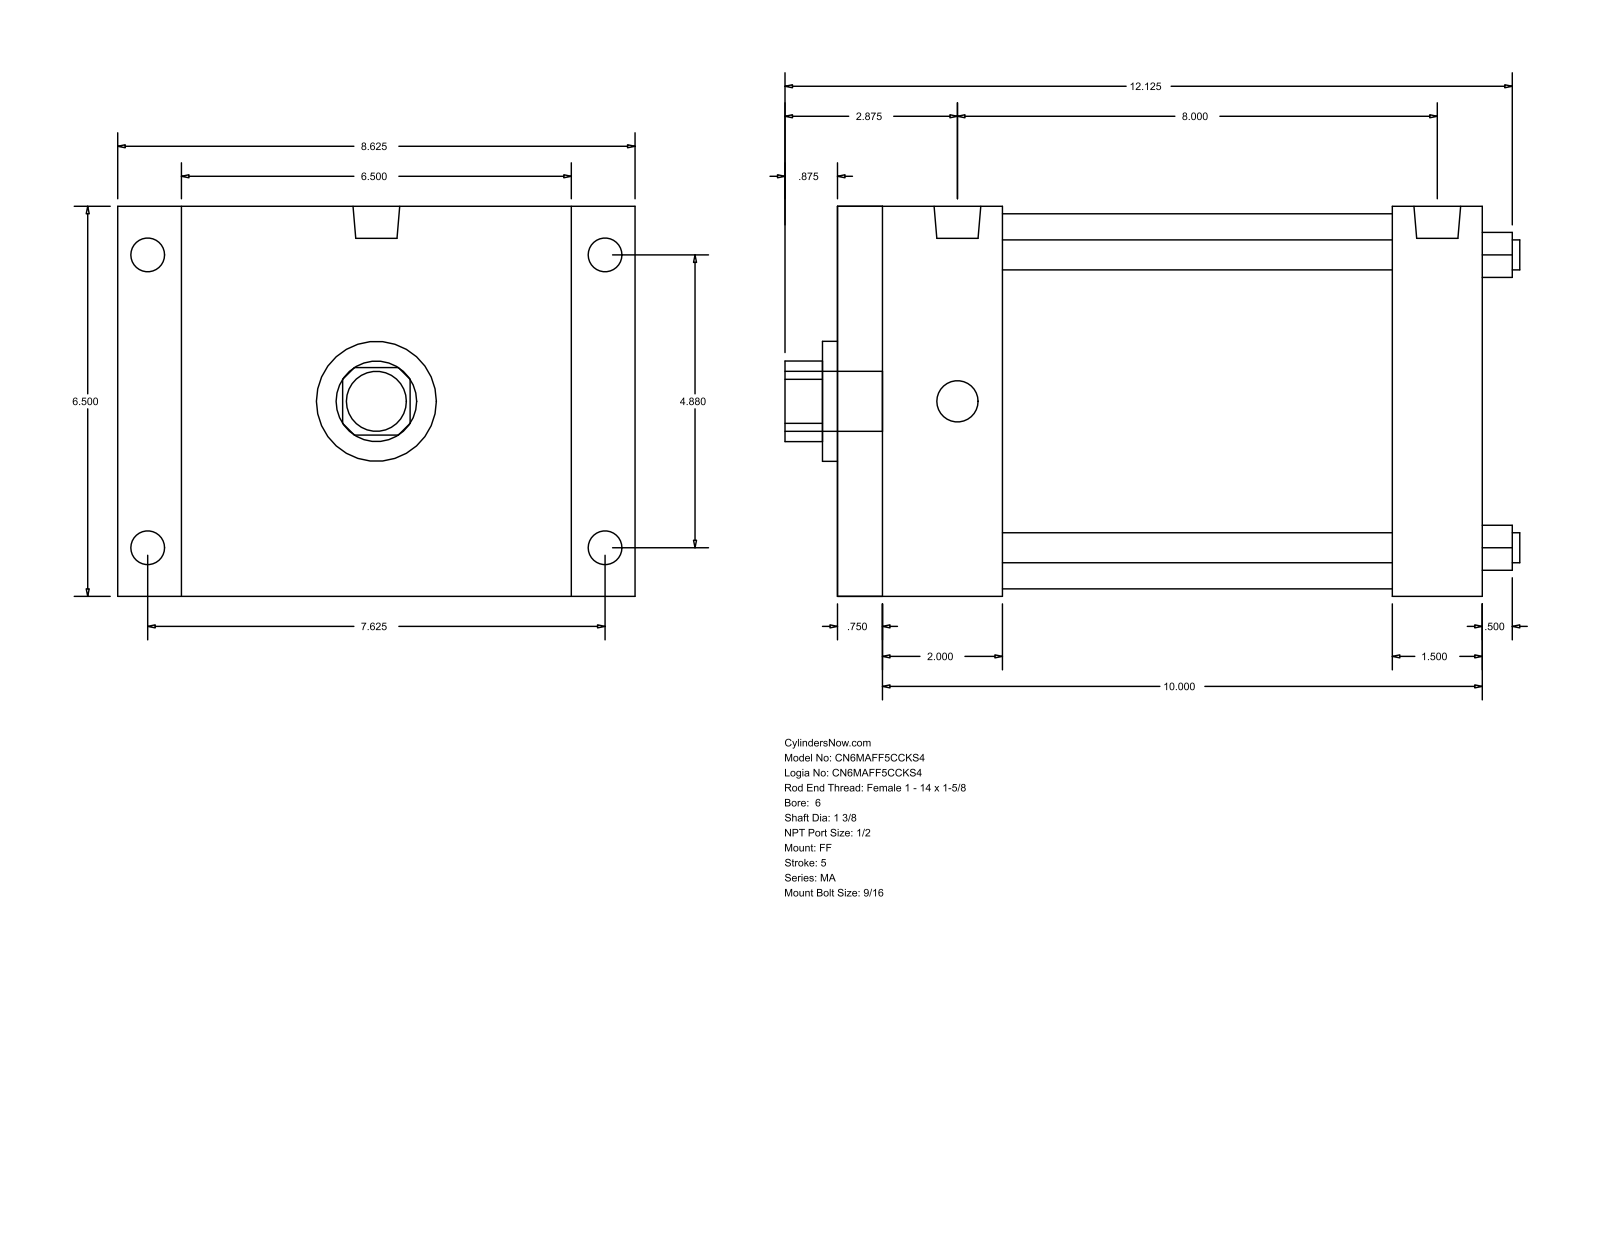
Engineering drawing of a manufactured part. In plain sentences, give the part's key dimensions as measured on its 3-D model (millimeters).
The part is named "MA_FF__0600_1.375". Its 3-D file was written by "GSSL Pune (CONFIG_CONTROL_DESIGN)". It is 0 solids with 92 faces: 64 planar, 28 cylindrical and 0 other. Overall it measures 311.15 by 219.07 by 165.1 millimeters. Round holes: 4 of diameter 12.7, 1 of diameter 34.92, 1 of diameter 50.8, 1 of diameter 158.75. Round bosses or shafts: 4 of diameter 17.46, 4 of diameter 14.29, 2 of diameter 19.77, 1 of diameter 25.4. Partial cylindrical surfaces (rounded edges, fillets, slot ends): 1 of radius 17.06. The main face-to-face distances are 165.1, 273.04, 219.08, 15.87, 257.17, 50.8, 66.67, 206.37, 234.95, 168.28. The hole center spacings are 87.65, 123.96, 175.31.
